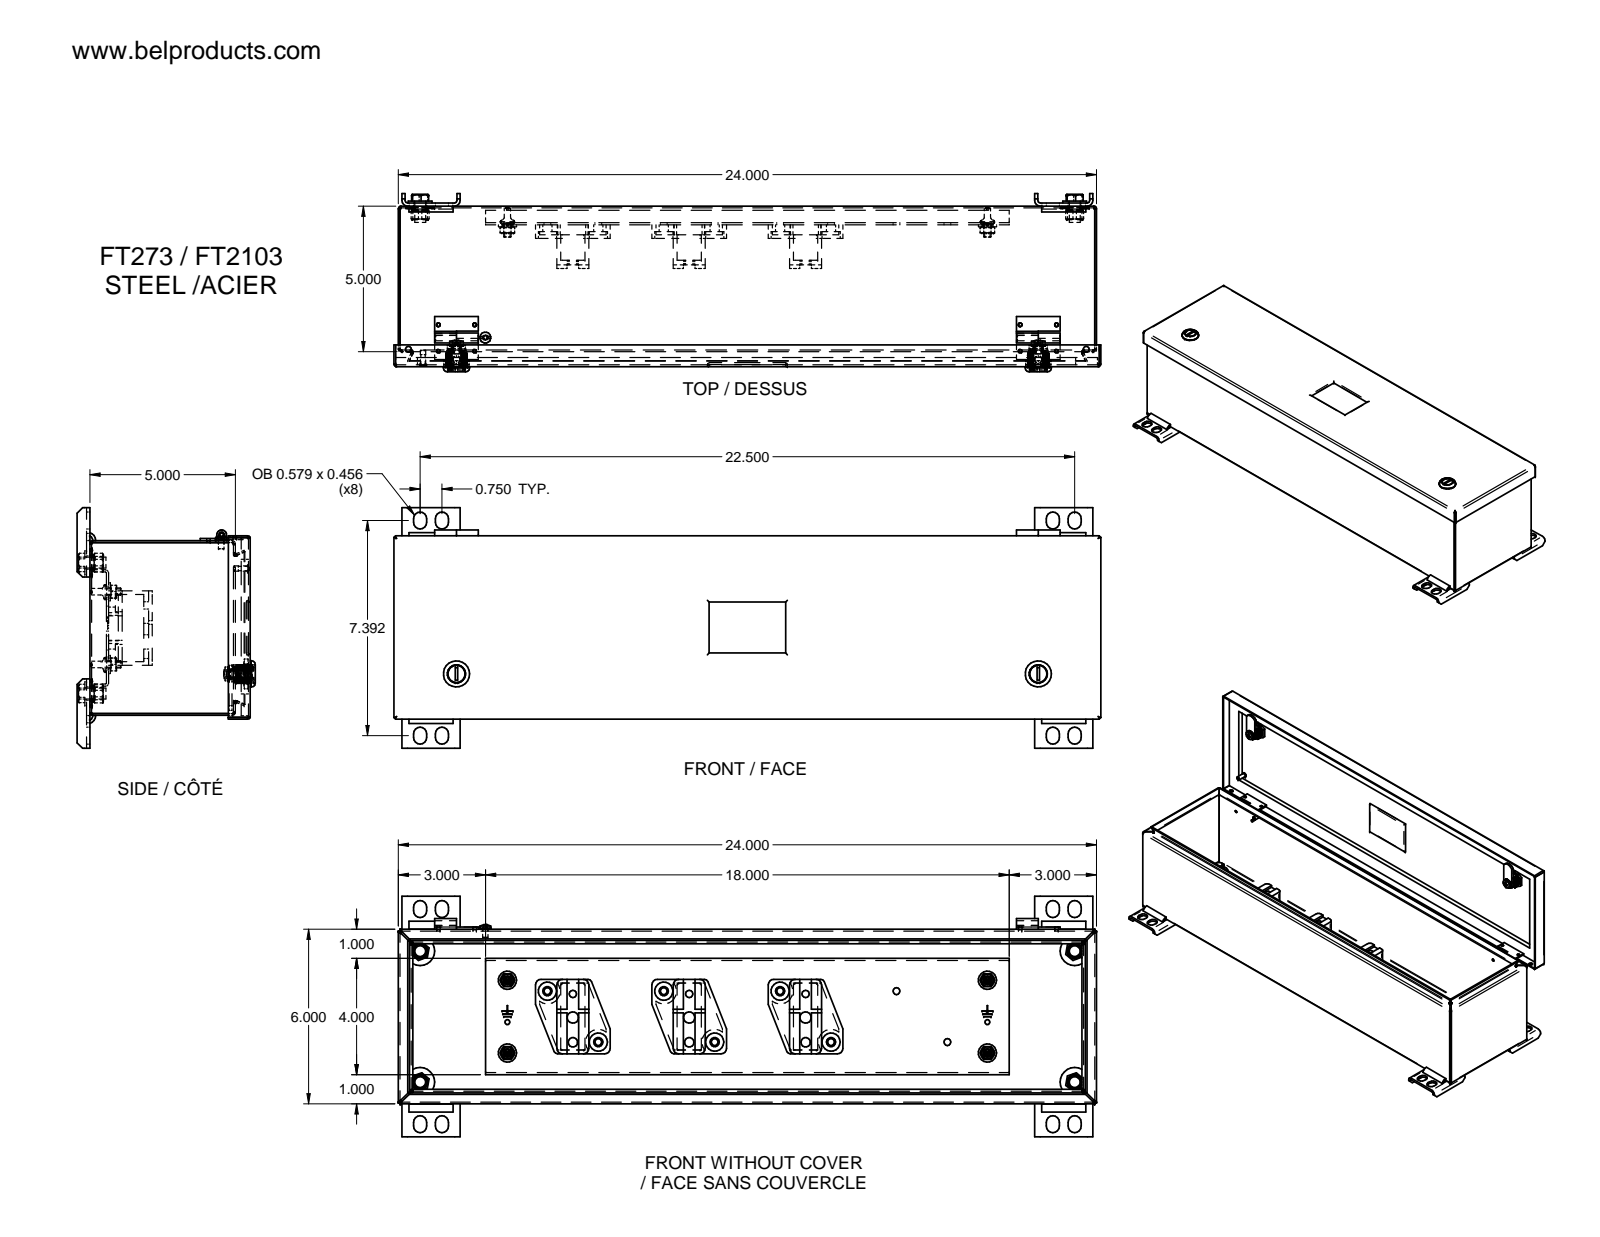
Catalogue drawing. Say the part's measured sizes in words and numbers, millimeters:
The part is named "0.375 DIA; CAOUTCHOUC; METAL; LOCK AVEC TOURNEVIS TYPE 4-12 SANS CAME-oa8 (+8 more)". Its 3-D file was written by "Unknown (AUTOMOTIVE_DESIGN)". It is 68 solids with 2464 faces: 1463 planar, 475 cylindrical and 526 other. Overall it measures 617.22 by 209.96 by 155.57 millimeters. Its volume is 1 135 000 cubic millimeters and its surface area 1 206 000 square millimeters. Round holes: 8 of diameter 3.16, 8 of diameter 3.3, 8 of diameter 5.99, 8 of diameter 9.53, 8 of diameter 11.58, 7 of diameter 6.35, 6 of diameter 7.92, 6 of diameter 15.88, 5 of diameter 3.17, 4 of diameter 7.14, 4 of diameter 9.02, 4 of diameter 10.31. Round bosses or shafts: 8 of diameter 3.17, 5 of diameter 3.02, 4 of diameter 20.62, 4 of diameter 15.88, 4 of diameter 5.56, 4 of diameter 0.79, 2 of diameter 22.86, 2 of diameter 22.61. Partial cylindrical surfaces (rounded edges, fillets, slot ends): 22 of radius 4.76, 22 of radius 9.53, 18 of radius 0.81, 16 of radius 0.25, 16 of radius 2.34, 16 of radius 5.79, 12 of radius 1.46, 8 of radius 1.52. The main face-to-face distances are 1.52, 150.88, 1.53, 138.53, 140.06, 137.01, 138.54, 152.4, 149.36, 16.27. The hole center spacings are 101.6, 203.2, 62.86, 152.67, 22.36, 23.03, 508, 30.87.
